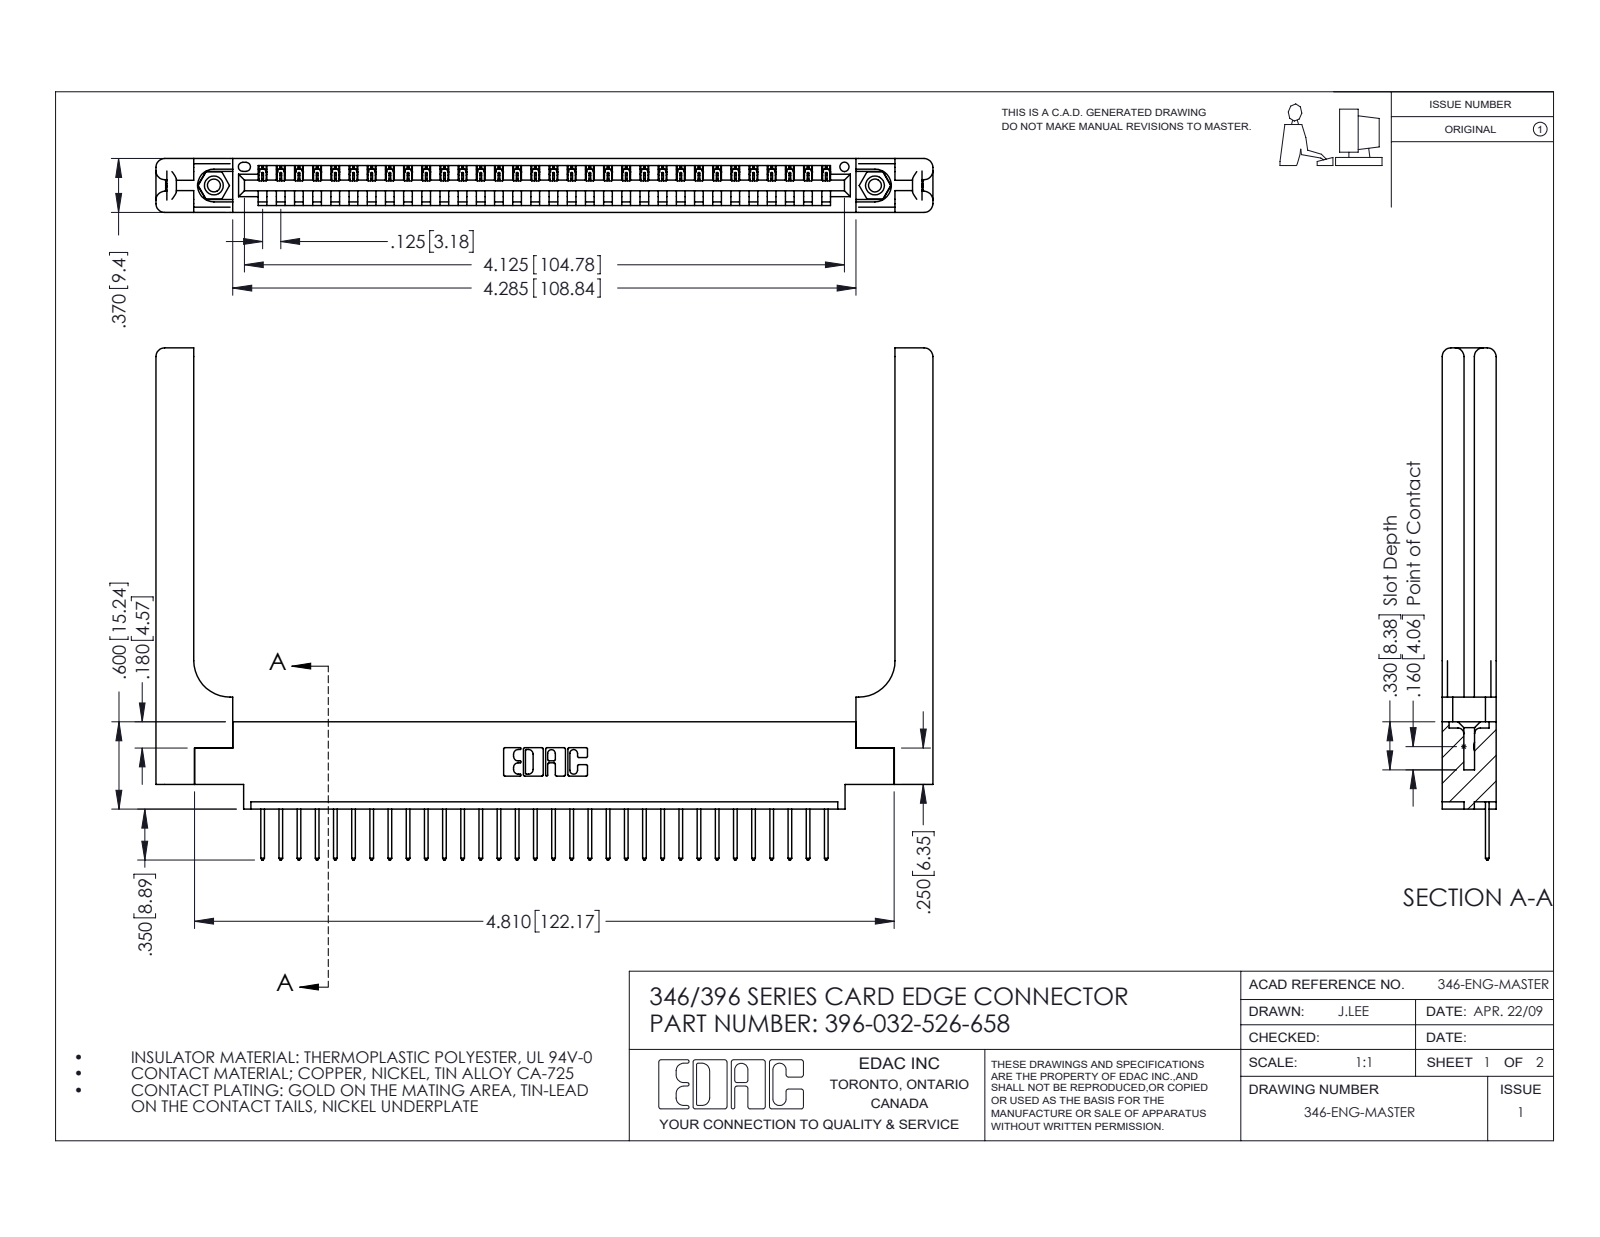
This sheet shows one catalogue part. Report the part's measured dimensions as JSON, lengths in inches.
{"part_name": "346-220-058_345-220-058; 345-292-001_345-293-126; 396-032-526-658; 346 Part_0.170 Offset - 0.156 Dia-TH (+1 more)", "step_written_by": "SolidWorks 2016 (CONFIG_CONTROL_DESIGN)", "units": "inches", "bodies": {"solids": 37, "faces": 2238, "planar": 1508, "cylindrical": 670, "other": 60}, "overall_size": [5.341, 3.52, 0.37], "volume_in3": 1.236, "surface_area_in2": 32.72, "round_holes": [[0.089, 2], [0.125, 2], [0.156, 2], [0.064, 1]], "round_bosses_or_shafts": [[0.155, 2]], "partial_cylinders_radius": [[0.006, 64], [0.01, 64], [0.01, 22], [0.06, 16], [0.007, 6], [0.031, 6], [0.026, 3], [0.03, 2]], "face_to_face_distances": [0.37, 0.048, 0.322, 0.072, 0.148, 0.15, 0.25, 0.298, 0.025, 0.222], "hole_center_spacings": [0.246, 4.337, 4.545]}
